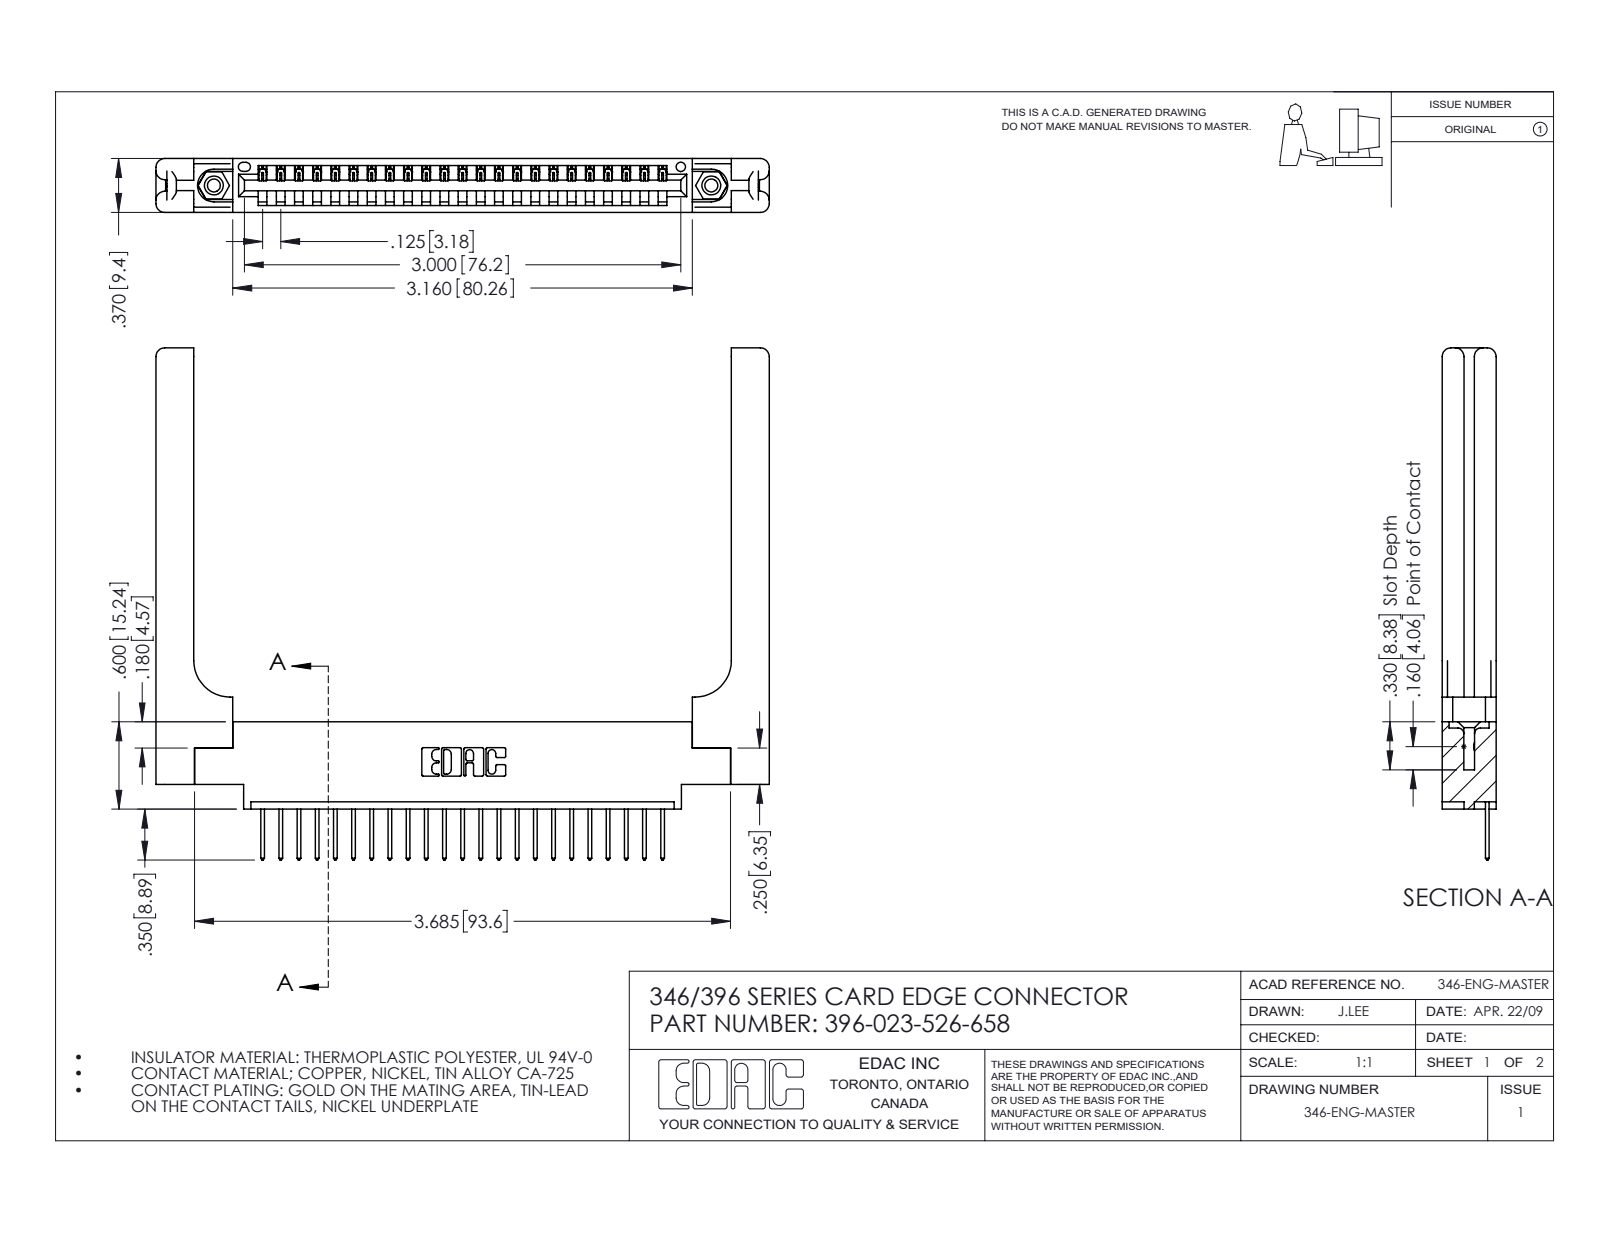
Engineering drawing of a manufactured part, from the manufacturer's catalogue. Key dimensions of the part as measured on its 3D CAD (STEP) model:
Part name (STEP PRODUCT): 396-023-526-658; 346 Part_0.170 Offset - 0.156 Dia-TH; 345-250-001_345-250-001-102; 345-292-001_345-293-126 (+1 more)
STEP written by: SolidWorks 2016 (CONFIG_CONTROL_DESIGN)
Units: inches
Bodies: 28 solids, 1716 faces (1148 planar, 508 cylindrical, 60 other)
Overall size (bounding box): 4.216 × 3.52 × 0.37
Volume: 1.066 in³ · Surface area: 27.18 in²
Round holes (diameter × count): ⌀0.089 ×2, ⌀0.125 ×2, ⌀0.156 ×2, ⌀0.064 ×1
Round bosses / shafts (diameter × count): ⌀0.155 ×2
Partial cylindrical surfaces — rounded edges, fillets, slot ends (radius × count): R0.006 ×46, R0.01 ×46, R0.01 ×22, R0.06 ×16, R0.007 ×6, R0.031 ×6, R0.026 ×3, R0.03 ×2
Main face-to-face distances: 0.37, 0.072, 0.048, 0.322, 0.15, 0.148, 0.25, 0.298, 0.025, 0.102
Hole centre spacings: 0.246, 3.212, 3.42
